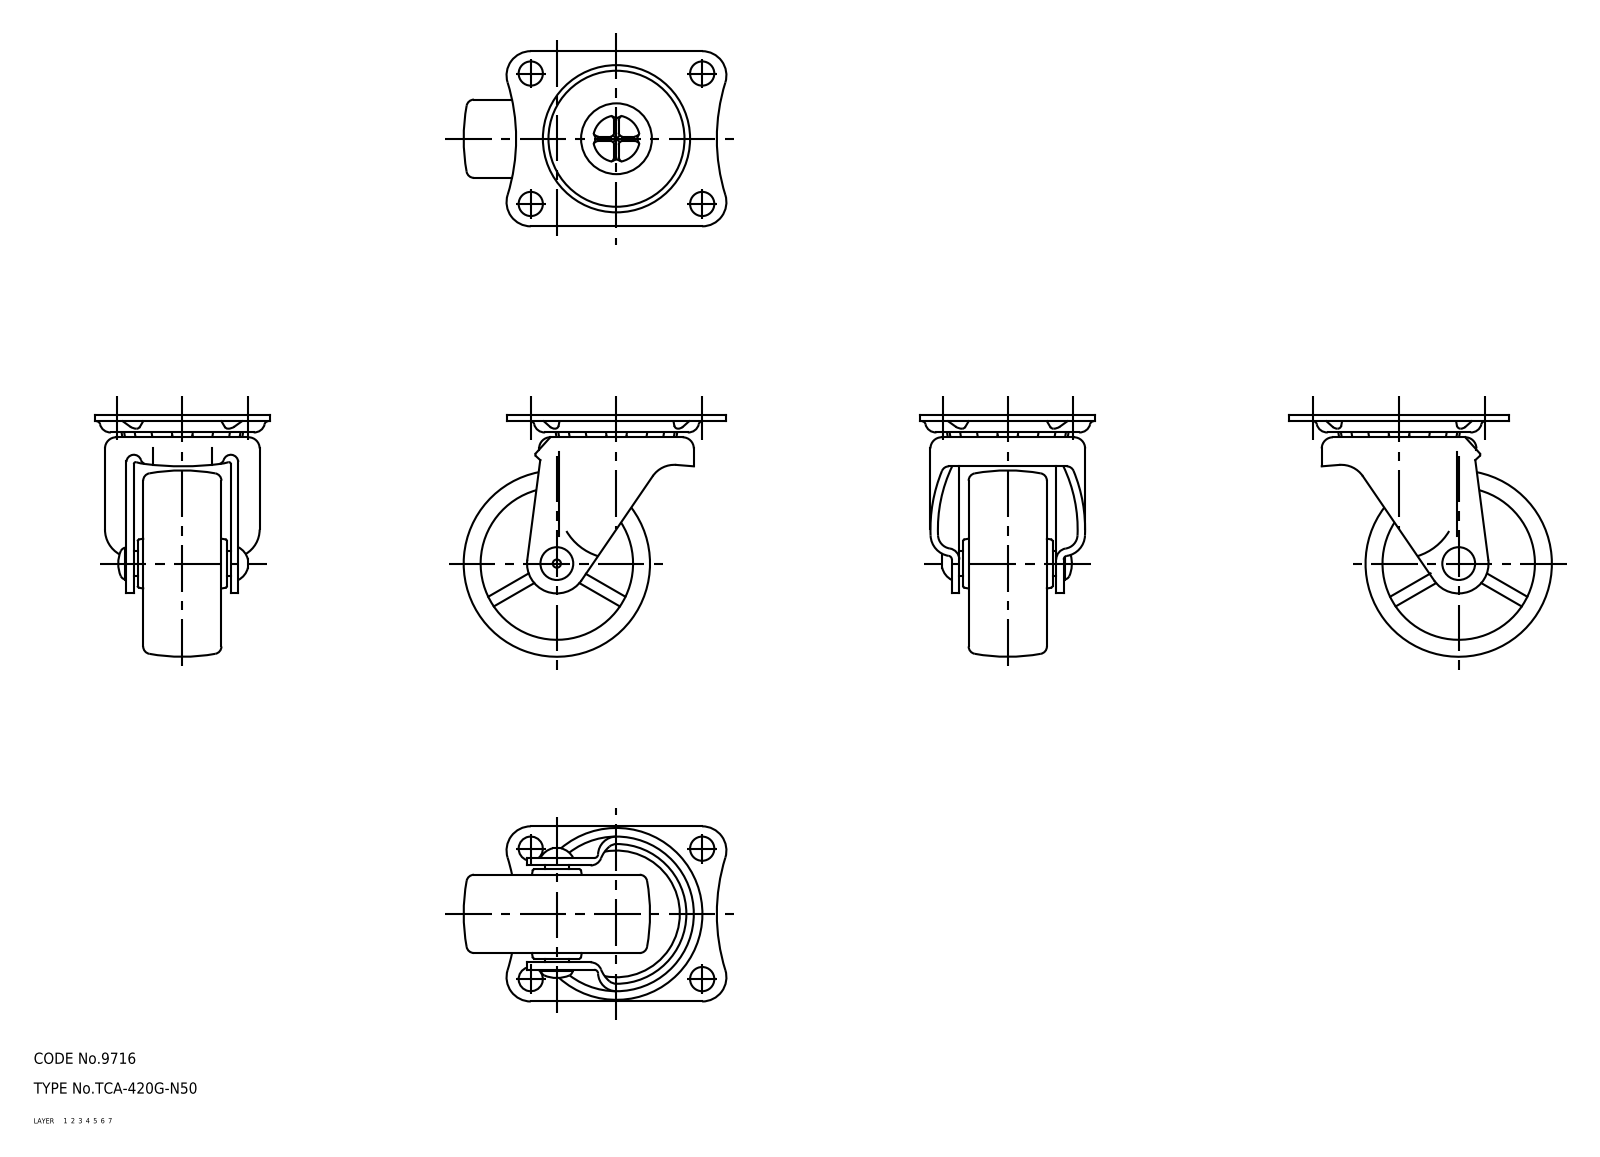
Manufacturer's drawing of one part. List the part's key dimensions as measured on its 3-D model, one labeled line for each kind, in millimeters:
Part name (STEP PRODUCT): wheel; mounting plate; main shaft; axle (+1 more)
STEP written by: CADfix (AUTOMOTIVE_DESIGN)
Units: millimetres
Bodies: 5 solids, 396 faces (0 planar, 0 cylindrical, 396 other)
Overall size (bounding box): 70.5 × 65 × 47
Volume: 42 848 mm³ · Surface area: 25 489 mm²
